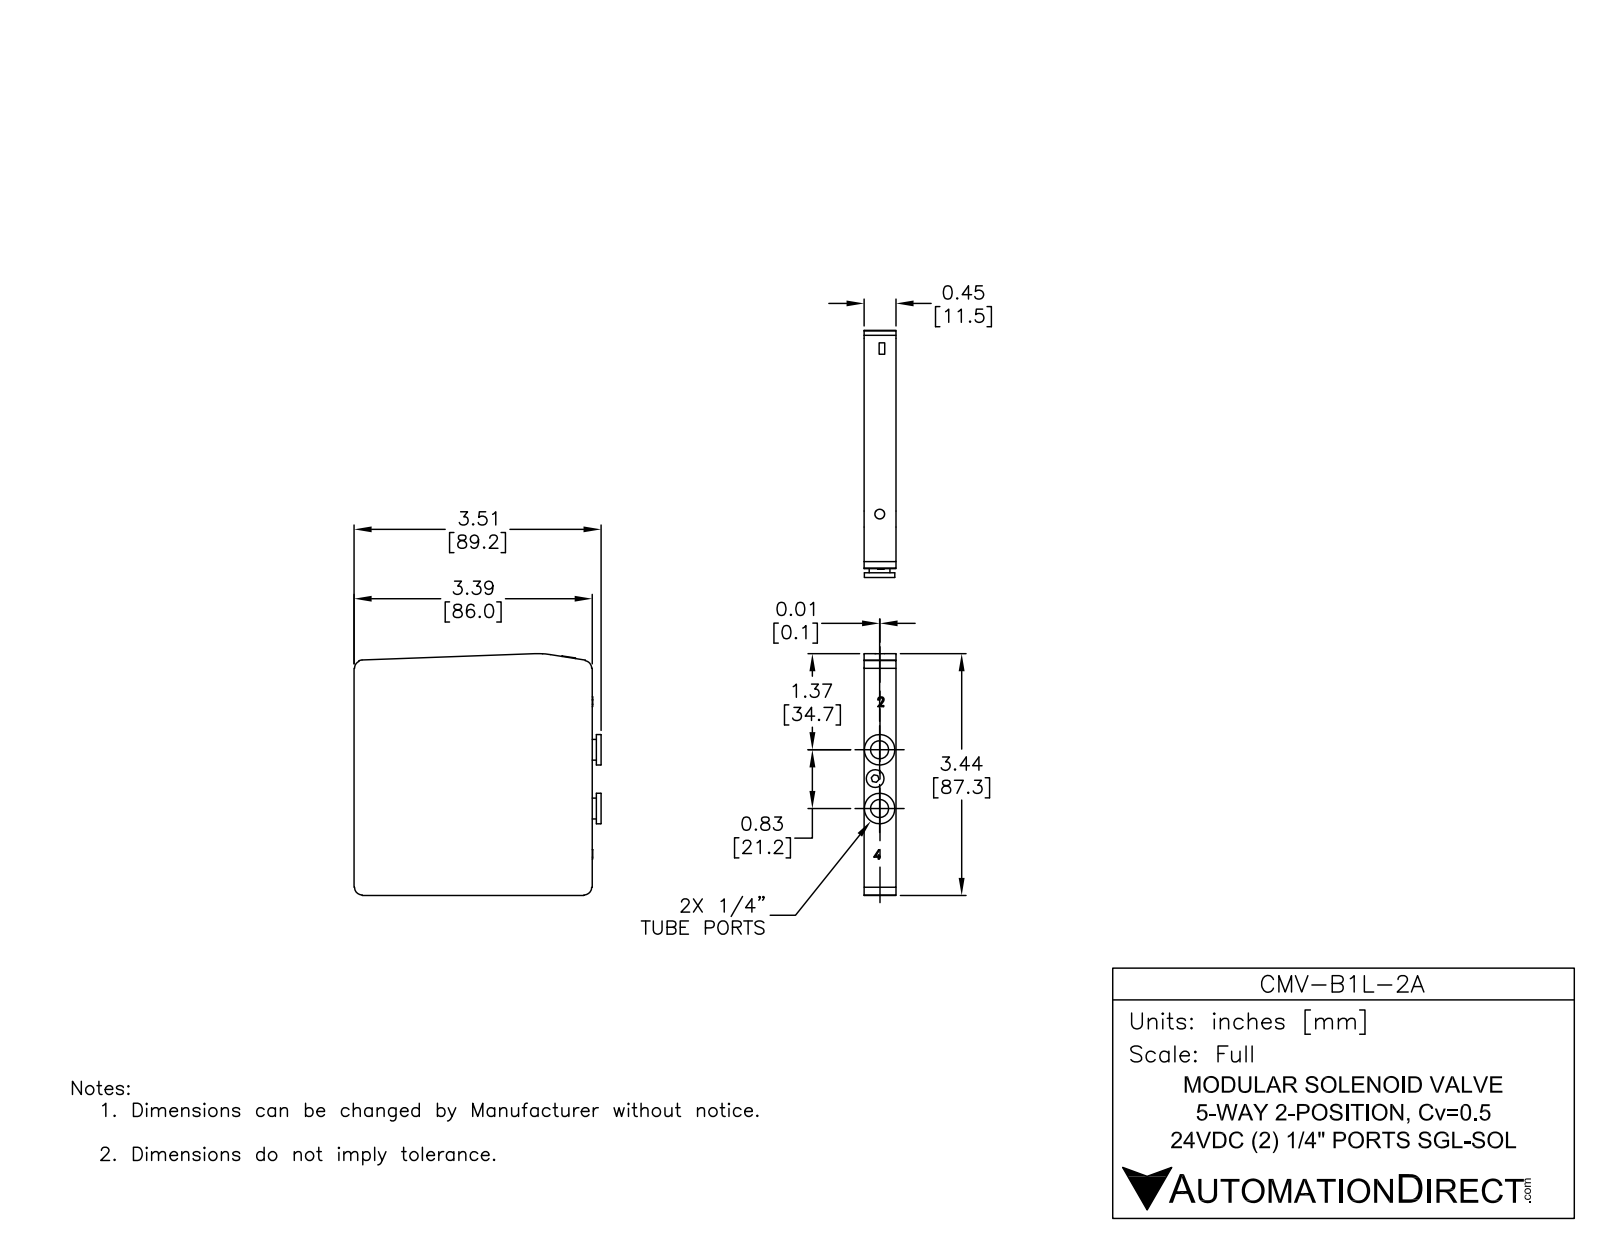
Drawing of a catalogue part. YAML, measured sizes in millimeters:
part_name: "CMV-B1L-2A"
step_written_by: "SolidWorks 2013 (AUTOMOTIVE_DESIGN)"
units: millimeters
bodies: {solids: 78, faces: 1133, planar: 870, cylindrical: 159, other: 104}
overall_size: [89.5, 87.3, 20.43]
volume: 78600
surface_area: 44630
round_holes:
  - {diameter: 5.25, count: 4}
  - {diameter: 6.5, count: 4}
  - {diameter: 4.4, count: 2}
  - {diameter: 8, count: 2}
  - {diameter: 9.5, count: 2}
  - {diameter: 3.35, count: 1}
  - {diameter: 3.6, count: 1}
  - {diameter: 6.25, count: 1}
round_bosses_or_shafts:
  - {diameter: 1.5, count: 4}
  - {diameter: 10.8, count: 2}
  - {diameter: 7.75, count: 2}
  - {diameter: 6.25, count: 2}
  - {diameter: 5.75, count: 2}
  - {diameter: 4.2, count: 2}
  - {diameter: 4, count: 2}
  - {diameter: 3.5, count: 1}
partial_cylinders:
  - {radius: 2.35, count: 12}
  - {radius: 0.78, count: 4}
  - {radius: 1, count: 4}
  - {radius: 1.5, count: 4}
  - {radius: 2.8, count: 4}
  - {radius: 0.15, count: 2}
  - {radius: 0.25, count: 2}
  - {radius: 0.17, count: 1}
face_to_face_distances: [11.5, 1.5, 10, 1, 3, 83, 2.5, 12.5, 10.83, 11.83]
hole_center_spacings: [9.7, 22.17, 8.66, 9.46, 10.28, 10.63, 11.02, 11.28]
